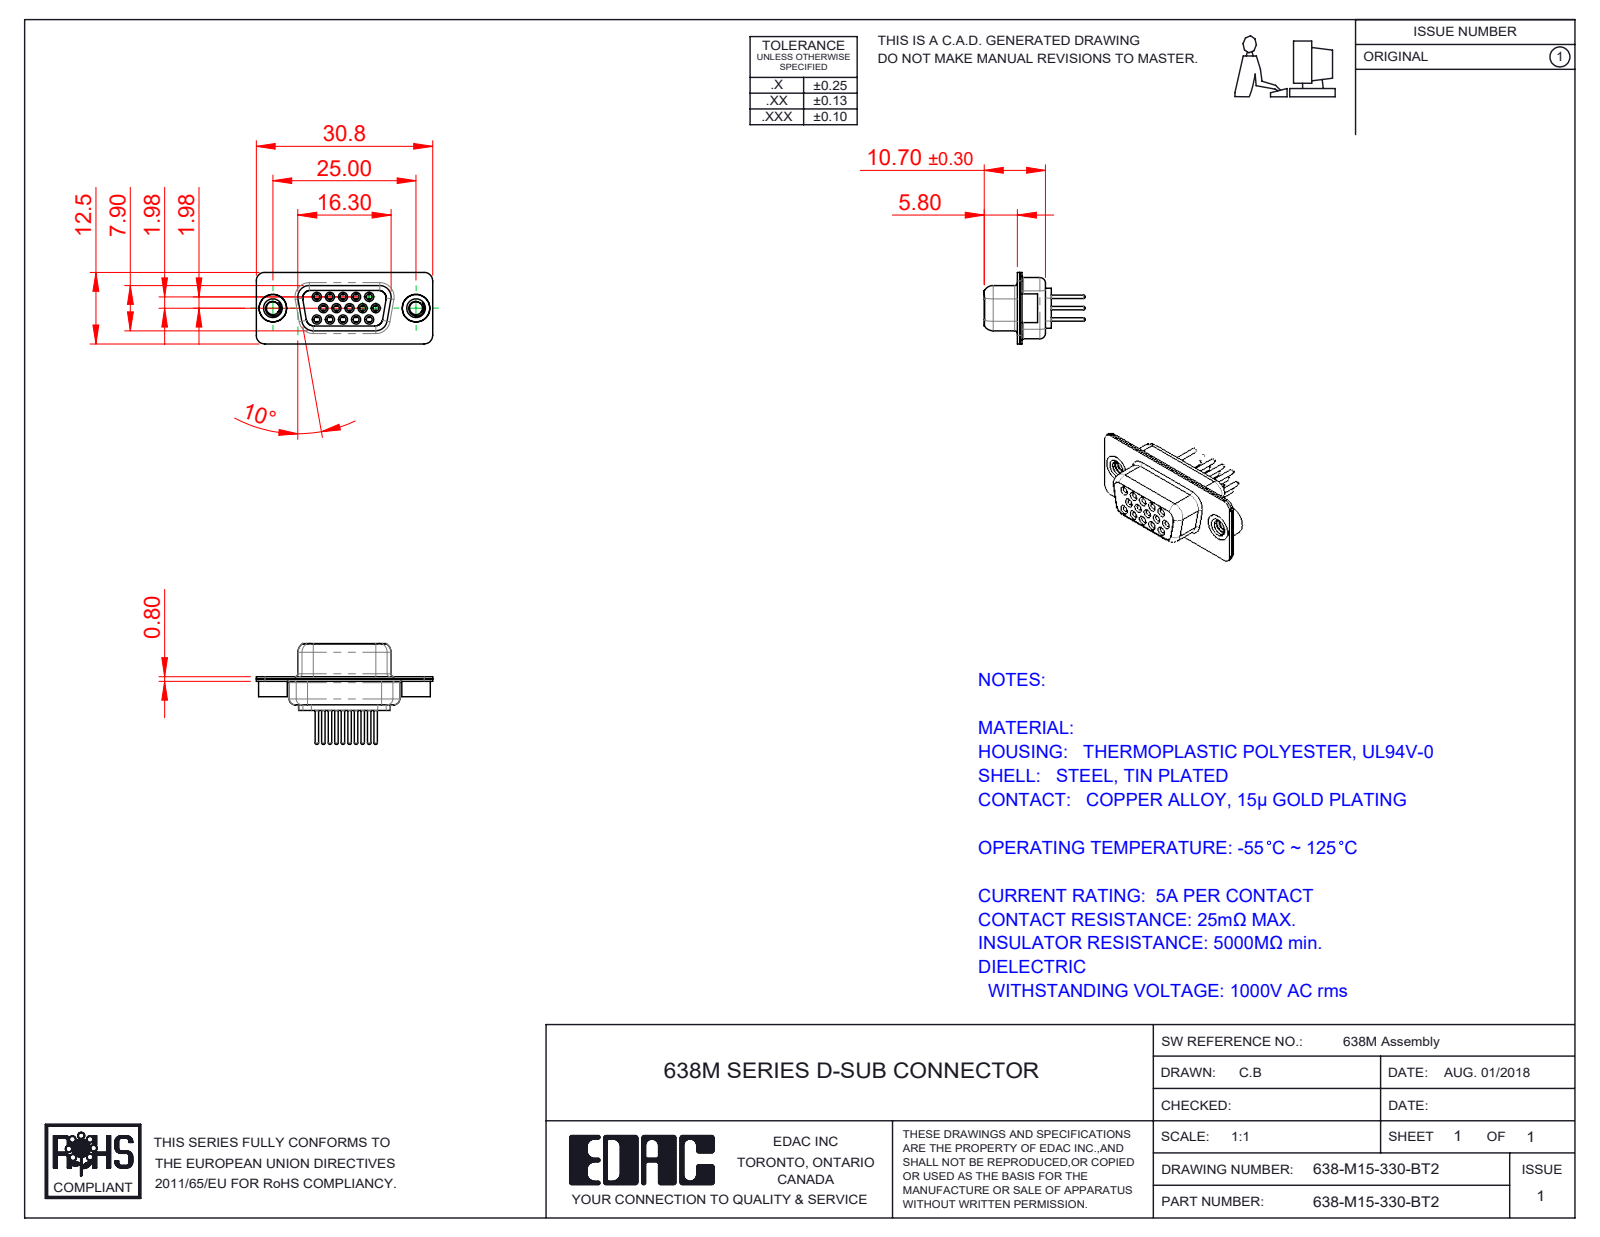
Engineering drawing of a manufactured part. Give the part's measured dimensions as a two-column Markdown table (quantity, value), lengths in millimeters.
| quantity | value |
| --- | --- |
| part name | 638M Shell Front_15 Contacts; 638M Shell Rear_15 Contacts; 638M Housing_15 Contacts; 638M Contact Row 2_30 (+4 more) |
| STEP written by | SolidWorks 2020 (CONFIG_CONTROL_DESIGN) |
| units | millimeters |
| bodies | 20 solids, 1104 faces (292 planar, 422 cylindrical, 390 other) |
| overall size | 30.8 × 17.6 × 12.5 |
| volume | 1 637 mm³ |
| surface area | 5 328 mm² |
| round holes (diameter × count) | 1 × 15, 1.1 × 15, 1.7 × 15, 1.8 × 15, 2 × 15, 2.26 × 2, 4 × 2, 4.8 × 2 |
| round bosses / shafts (diameter × count) | 2.2 × 15, 1.6 × 15, 1.5 × 15, 0.6 × 15, 5 × 2, 4.9 × 2 |
| partial cylindrical surfaces (radius × count) | 1.5 × 16, 2 × 12, 1.35 × 8, 1.6 × 8, 0.25 × 4, 0.5 × 4, 0.6 × 4, 0.65 × 4 |
| main face-to-face distances | 0.4, 1.4, 0.45, 8.45, 1, 0.8, 8.9, 1.8, 6.2, 9.3 |
| hole center spacings | 2.28, 3.96, 2.29, 4.57, 6.05, 6.04, 6.86, 7.92 |
